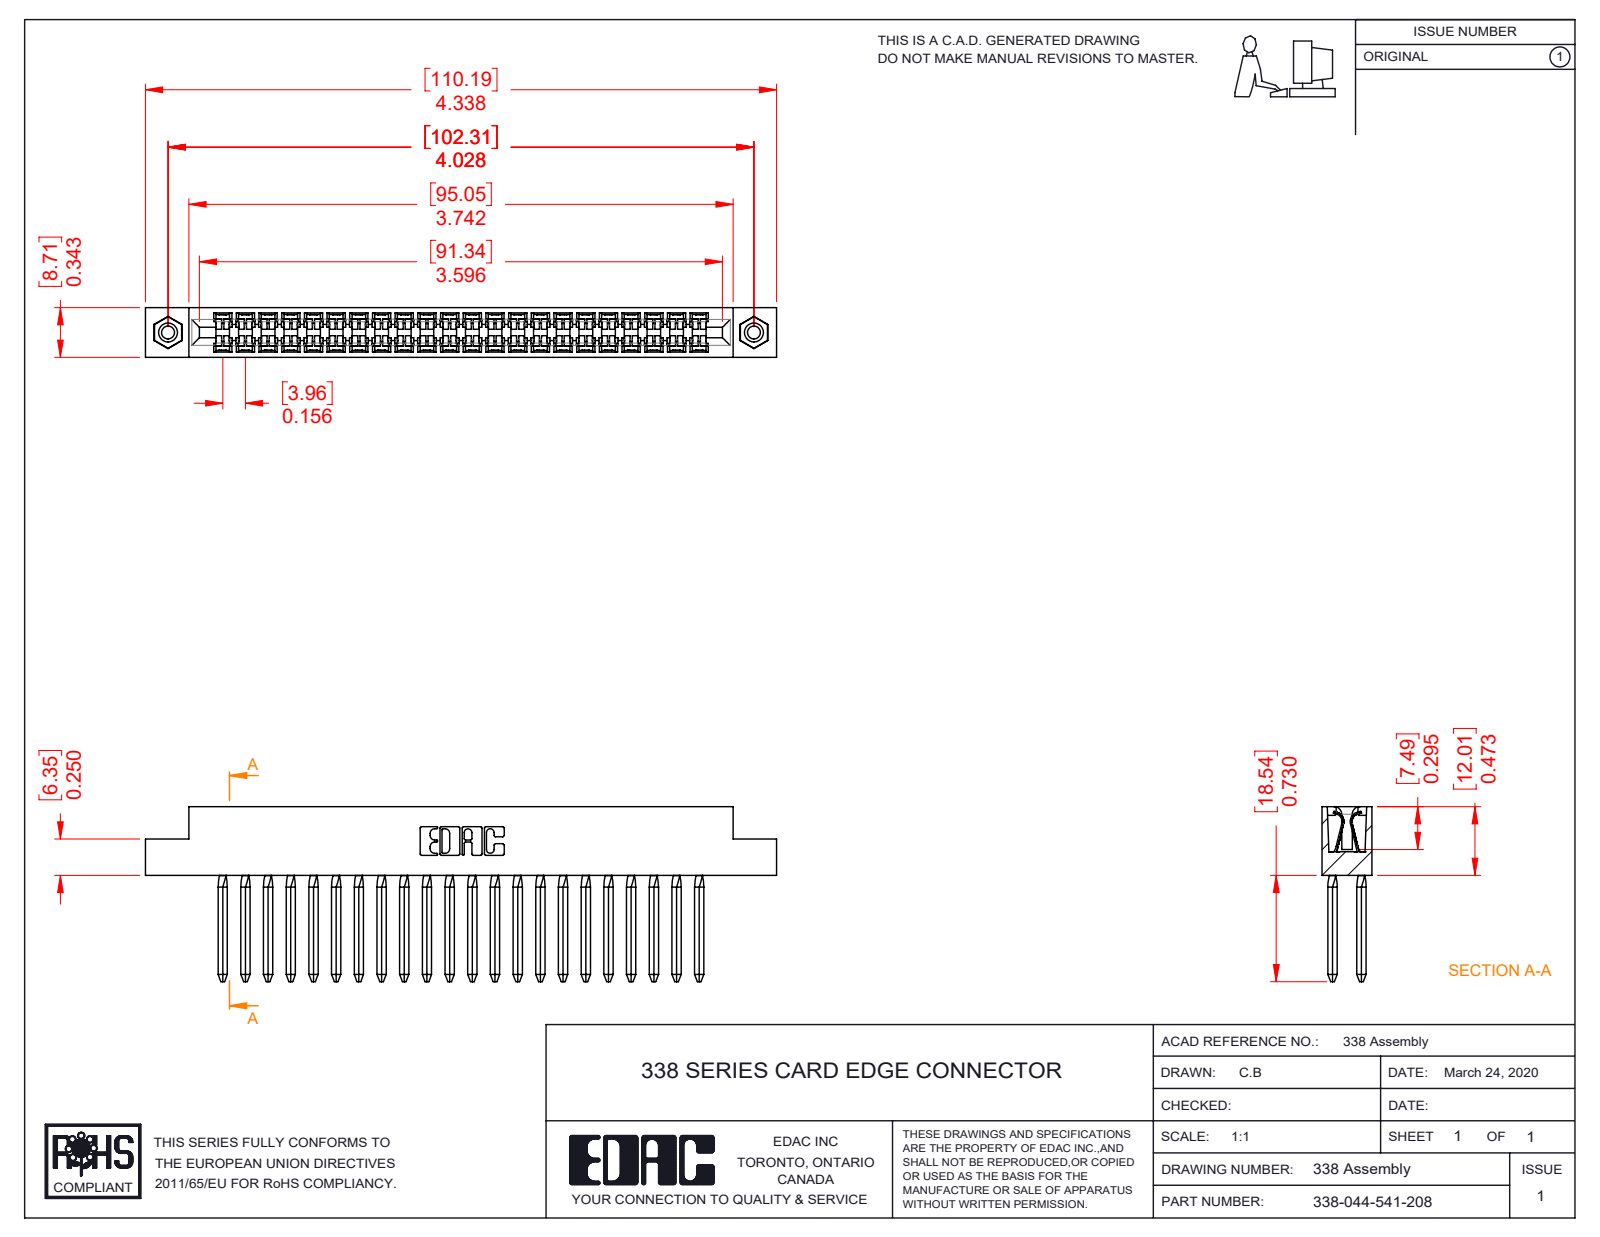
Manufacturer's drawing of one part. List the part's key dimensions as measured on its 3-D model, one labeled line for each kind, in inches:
Part name (STEP PRODUCT): 338-210-001_338-210-022-004; 338-290-001_541; 338-044-541-208; 345-250-001_345-250-003-102
STEP written by: SolidWorks 2016 (CONFIG_CONTROL_DESIGN)
Units: inches
Bodies: 47 solids, 3102 faces (2150 planar, 760 cylindrical, 192 other)
Overall size (bounding box): 4.338 × 1.203 × 0.343
Volume: 0.516 in³ · Surface area: 24.28 in²
Round holes (diameter × count): ⌀0.089 ×2, ⌀0.125 ×2, ⌀0.156 ×2
Round bosses / shafts (diameter × count): ⌀0.155 ×2
Partial cylindrical surfaces — rounded edges, fillets, slot ends (radius × count): R0.025 ×134, R0.008 ×44, R0.055 ×36, R0.067 ×36, R0.1 ×35, R0.01 ×22, R0.007 ×6, R0.031 ×6
Main face-to-face distances: 0.343, 0.156, 0.11, 0.624, 0.207, 0.135, 0.78, 0.468, 0.221, 0.441
Hole centre spacings: 4.028
